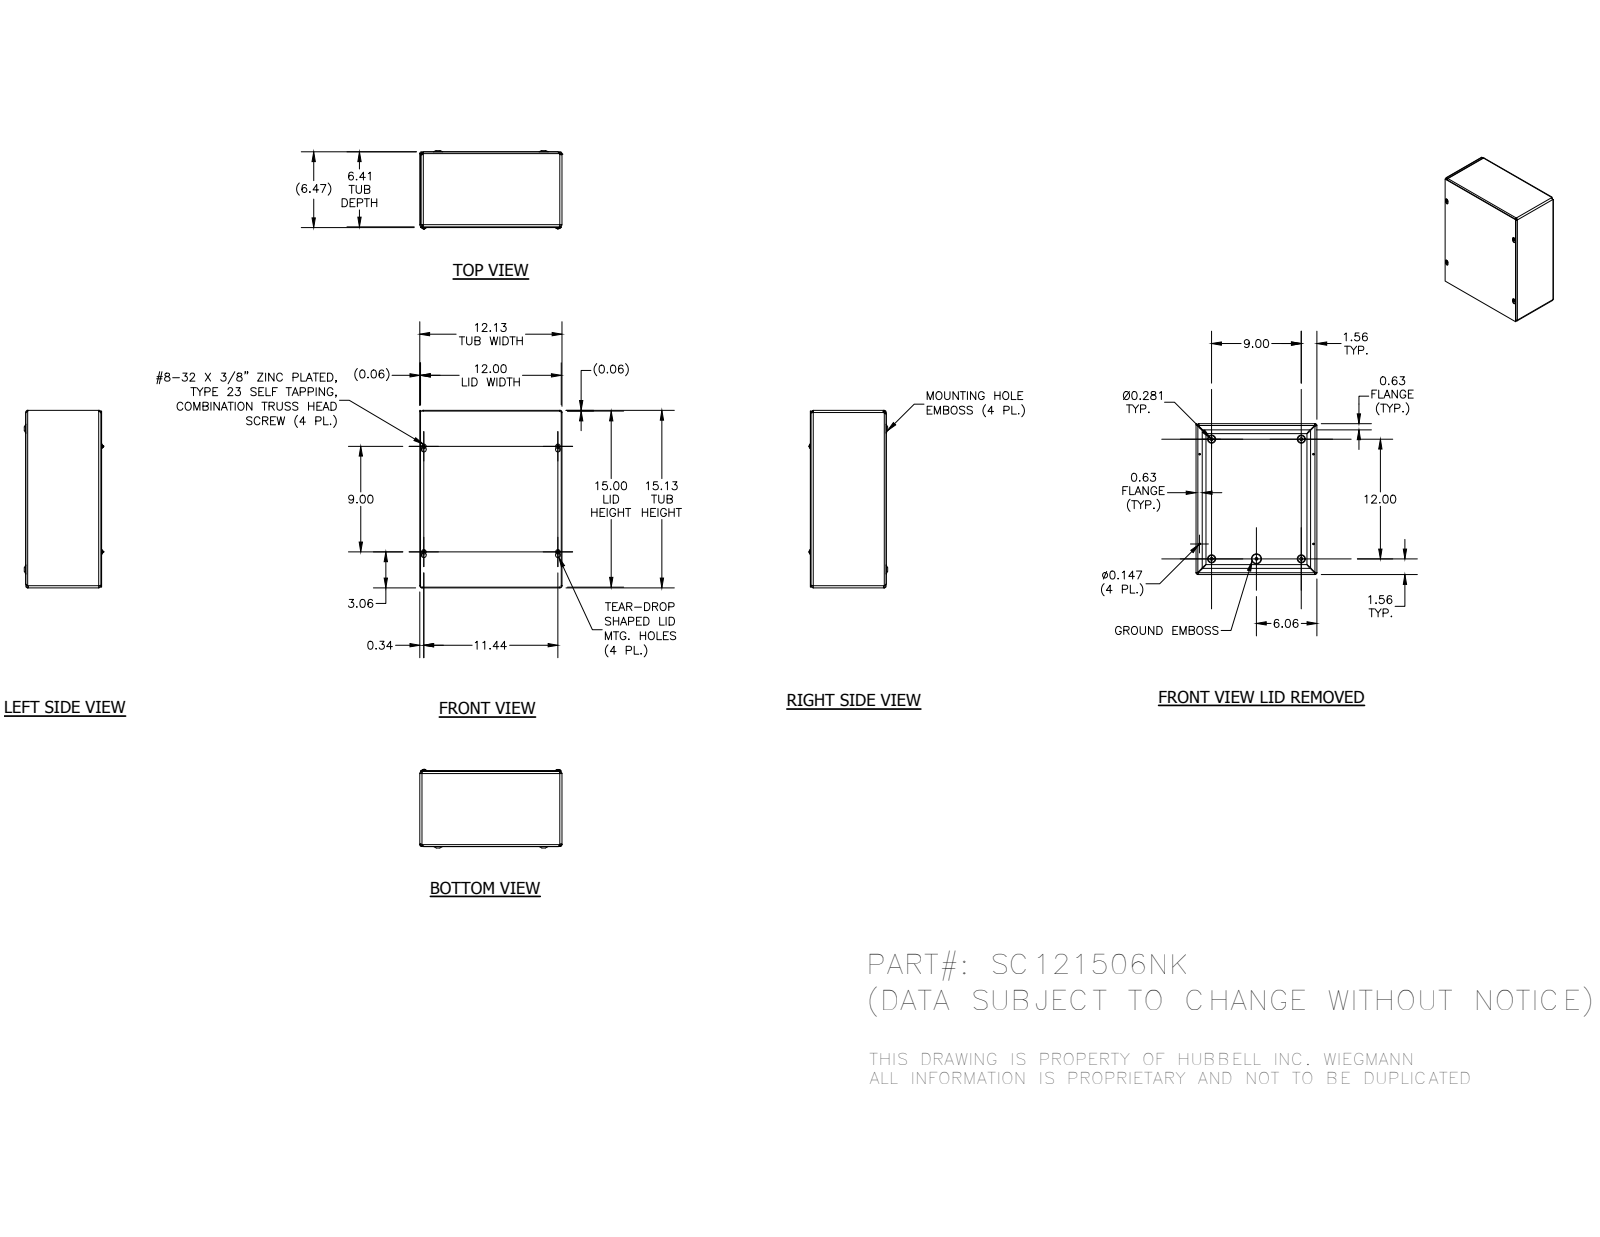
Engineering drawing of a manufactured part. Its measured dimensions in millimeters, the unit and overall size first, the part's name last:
Units: millimetres
Overall size (bounding box): 384.18 × 307.98 × 170
Round holes (diameter × count): ⌀3.73 ×4, ⌀7.62 ×4, ⌀4.19 ×1
Round bosses / shafts (diameter × count): ⌀9.75 ×4, ⌀4.17 ×4, ⌀5.8 ×1
Partial cylindrical surfaces — rounded edges, fillets, slot ends (radius × count): R3.17 ×12, R4.75 ×8, R1.4 ×4, R1.57 ×4, R2.38 ×4, R2.97 ×4, R3.15 ×4, R3.96 ×4
Main face-to-face distances: 1.57, 161.12, 1.58, 162.69, 1.59, 162.71, 164.28, 306.4, 307.98, 304.83
Hole centre spacings: 49.09, 228.6, 268.49, 114.3, 262.33, 262.34, 290.51, 303.69
Volume: 782 909 mm³ · Surface area: 1 003 000 mm²
Bodies: 7 solids, 357 faces (132 planar, 67 cylindrical, 158 other)
Part name (STEP PRODUCT): SC1215BKP; SC121506NKWRA; SC1215LID; 34056 (+1 more)
STEP written by: Autodesk Inventor 2014 (AUTOMOTIVE_DESIGN)
